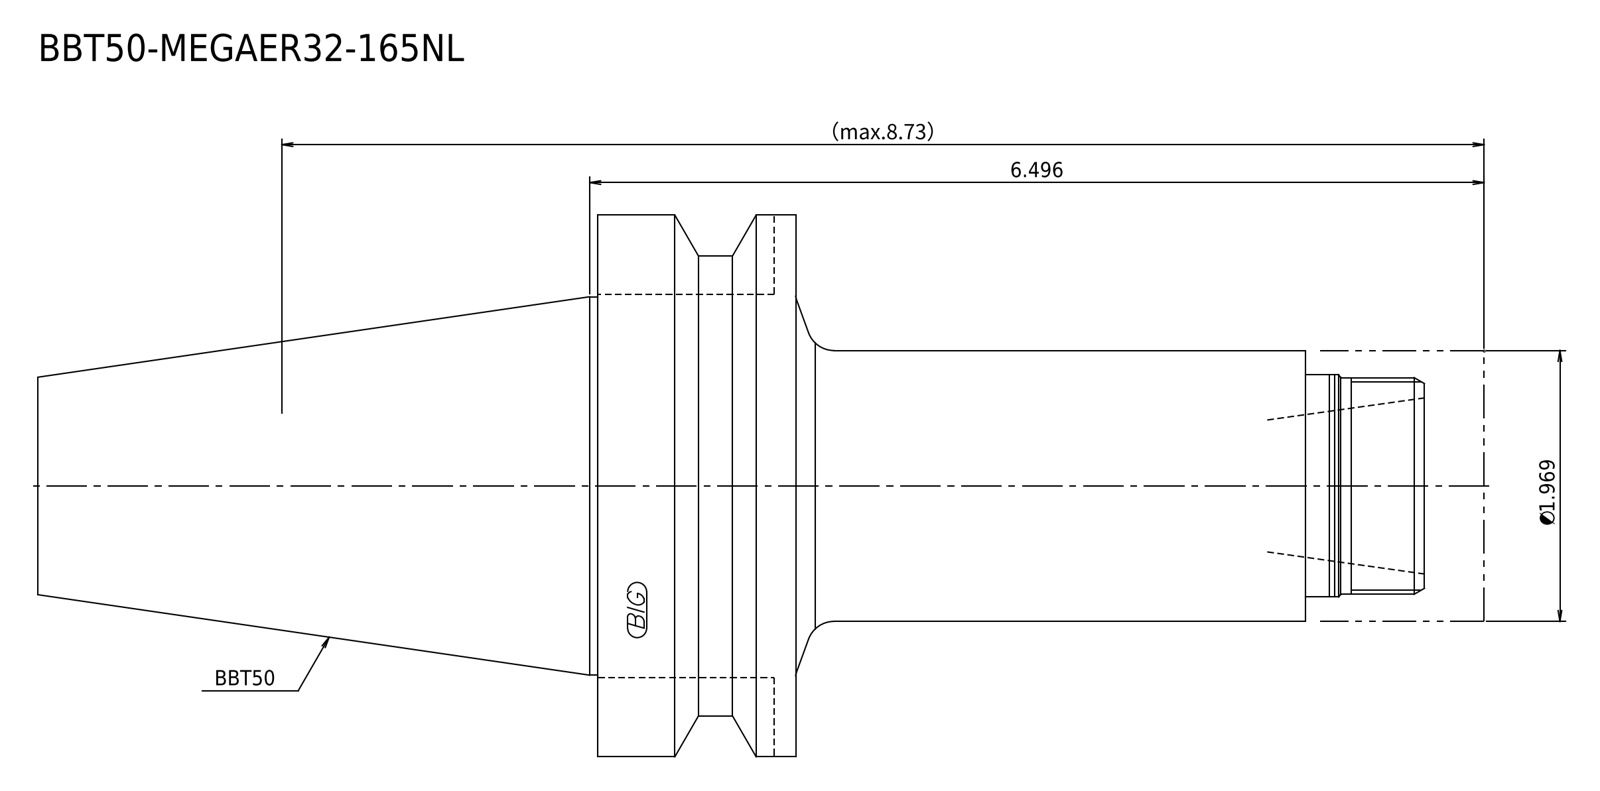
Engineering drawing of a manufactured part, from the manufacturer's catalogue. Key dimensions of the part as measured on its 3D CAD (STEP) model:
STEP written by: Kubotek KeyCreator 2011 V10.0.2 (22737) (automotive_design)
Units: inches
Bodies: 2 solids, 21 faces (7 planar, 8 cylindrical, 6 other)
Overall size (bounding box): 266.8 × 100 × 100
Volume: 794 855 in³ · Surface area: 70 128 in²
Round bosses / shafts (diameter × count): ⌀100 ×1, ⌀85 ×1, ⌀69.85 ×1, ⌀50 ×1, ⌀41 ×1, ⌀40 ×1
Main face-to-face distances: 36.5, 127, 163.5, 30.2, 96.8, 133.3, 266.8, 236.6, 139.8, 103.3
